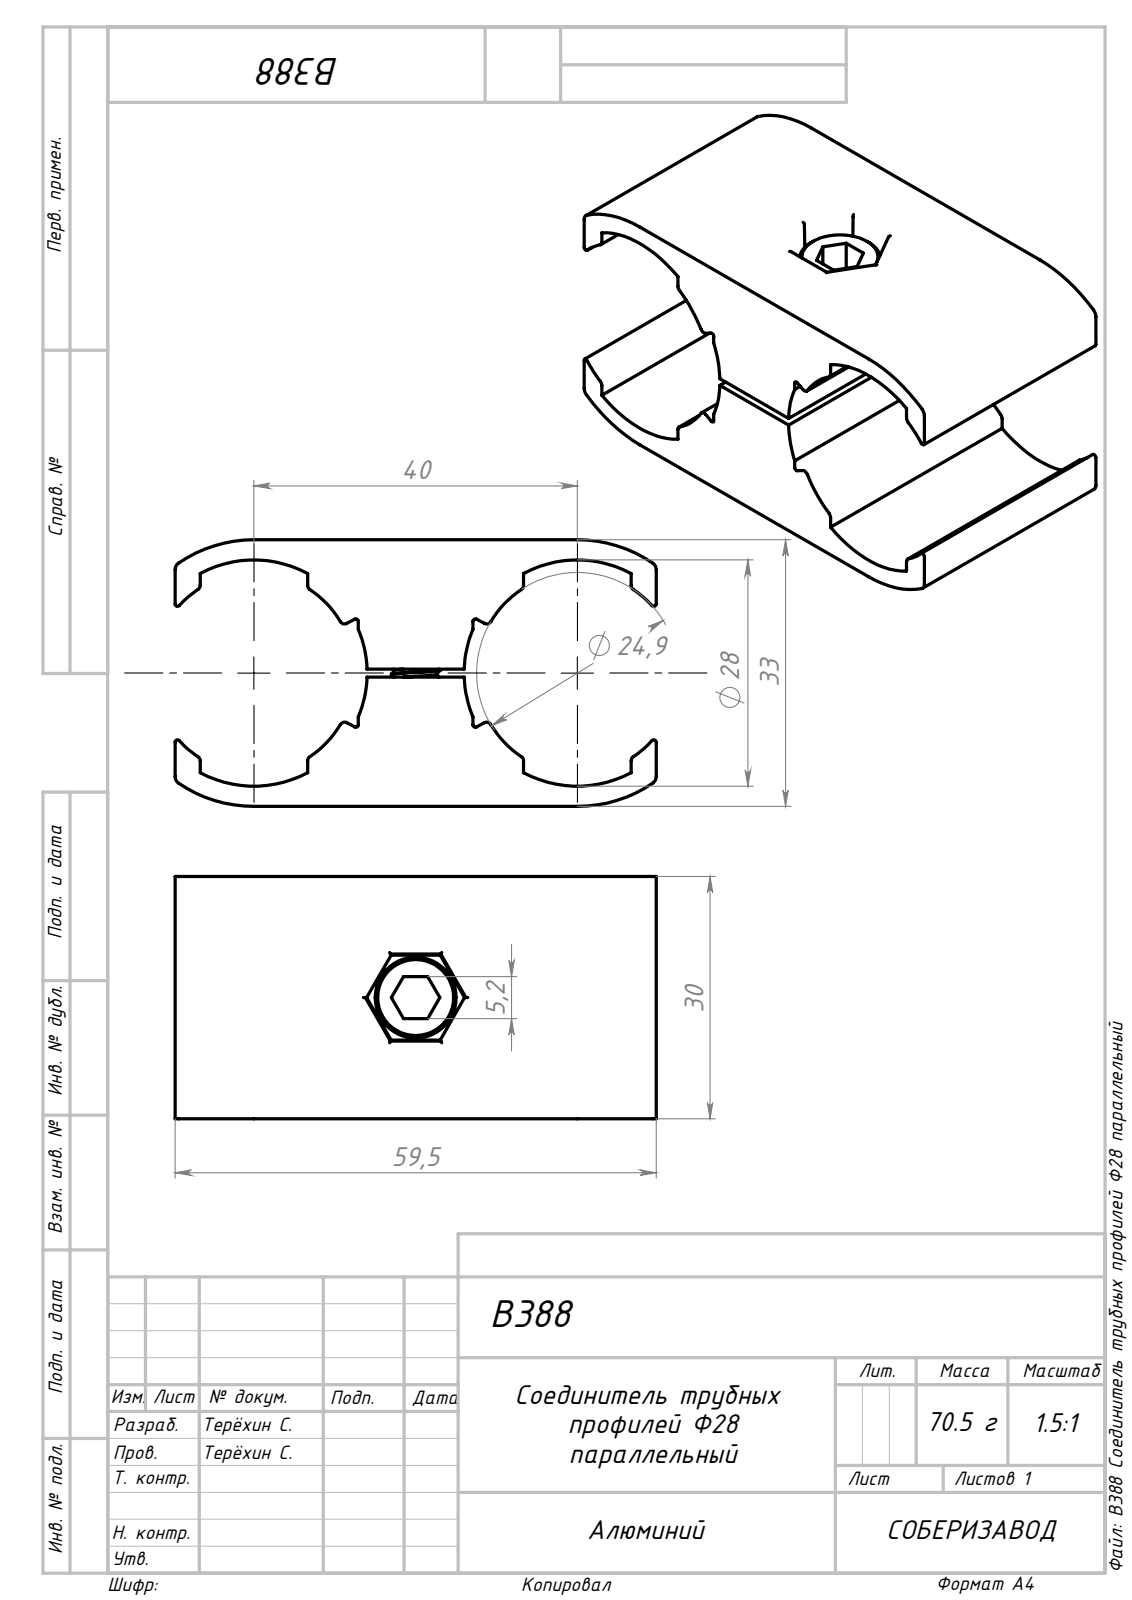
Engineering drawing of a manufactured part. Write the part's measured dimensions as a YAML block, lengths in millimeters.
part_name: "B388 Соединитель трубных профилей Ф28 параллельный"
step_written_by: "SolidWorks 2022 (AUTOMOTIVE_DESIGN)"
units: millimeters
bodies: {solids: 4, faces: 227, planar: 60, cylindrical: 118, other: 49}
overall_size: [59.5, 33, 30]
volume: 25297
surface_area: 13209
round_holes:
  - {diameter: 5.2, count: 1}
  - {diameter: 6.5, count: 1}
round_bosses_or_shafts:
  - {diameter: 10, count: 1}
  - {diameter: 6, count: 1}
partial_cylinders:
  - {radius: 0.2, count: 12}
  - {radius: 0.6, count: 12}
  - {radius: 0.3, count: 8}
  - {radius: 1, count: 4}
  - {radius: 12.45, count: 2}
  - {radius: 14, count: 2}
  - {radius: 16.5, count: 2}
face_to_face_distances: [33, 30, 17, 16, 8, 1, 59.5, 10, 25, 9]
